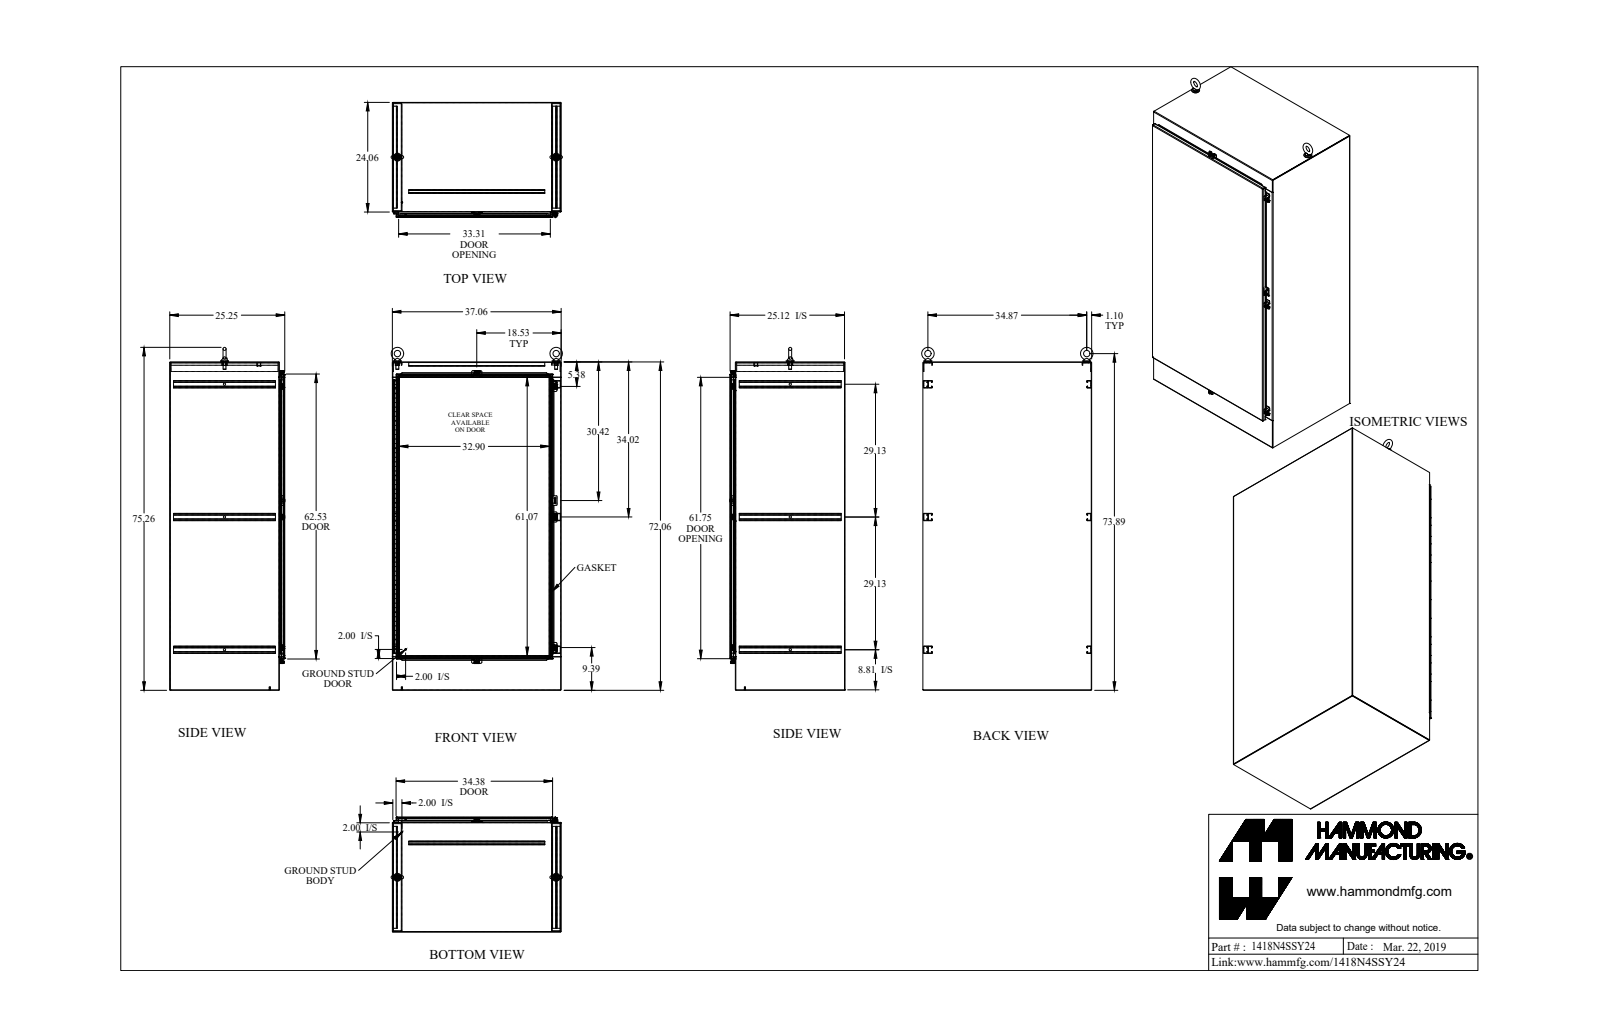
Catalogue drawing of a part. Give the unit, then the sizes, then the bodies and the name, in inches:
Units: inches
Overall size (bounding box): 75.719 × 38.118 × 25.31
Round holes (diameter × count): ⌀0.304 ×10, ⌀0.213 ×5, ⌀0.265 ×5, ⌀0.375 ×5, ⌀0.5 ×3, ⌀0.527 ×2, ⌀0.625 ×2, ⌀0.68 ×2, ⌀0.75 ×2, ⌀0.11 ×1, ⌀0.125 ×1
Round bosses / shafts (diameter × count): ⌀0.5 ×5, ⌀0.39 ×5, ⌀0.244 ×5, ⌀1.75 ×2, ⌀1.5 ×2, ⌀1.25 ×2, ⌀0.738 ×2, ⌀0.313 ×2
Partial cylindrical surfaces — rounded edges, fillets, slot ends (radius × count): R0.043 ×60, R0.138 ×54, R0.048 ×39, R0.143 ×39, R0.25 ×26, R0.06 ×10, R0.141 ×10, R0.125 ×8
Main face-to-face distances: 0.095, 25.152, 36.965, 25.057, 25.247, 36.87, 71.965, 37.06, 1.187, 23.965
Hole centre spacings: 6, 12, 18, 24, 30, 36, 42, 29.13
Volume: 1 187 in³ · Surface area: 25 181 in²
Bodies: 53 solids, 2016 faces (1080 planar, 840 cylindrical, 96 other)
Part name (STEP PRODUCT): 1418N4SSY24_Default
STEP written by: SolidWorks 2019 (CONFIG_CONTROL_DESIGN)
